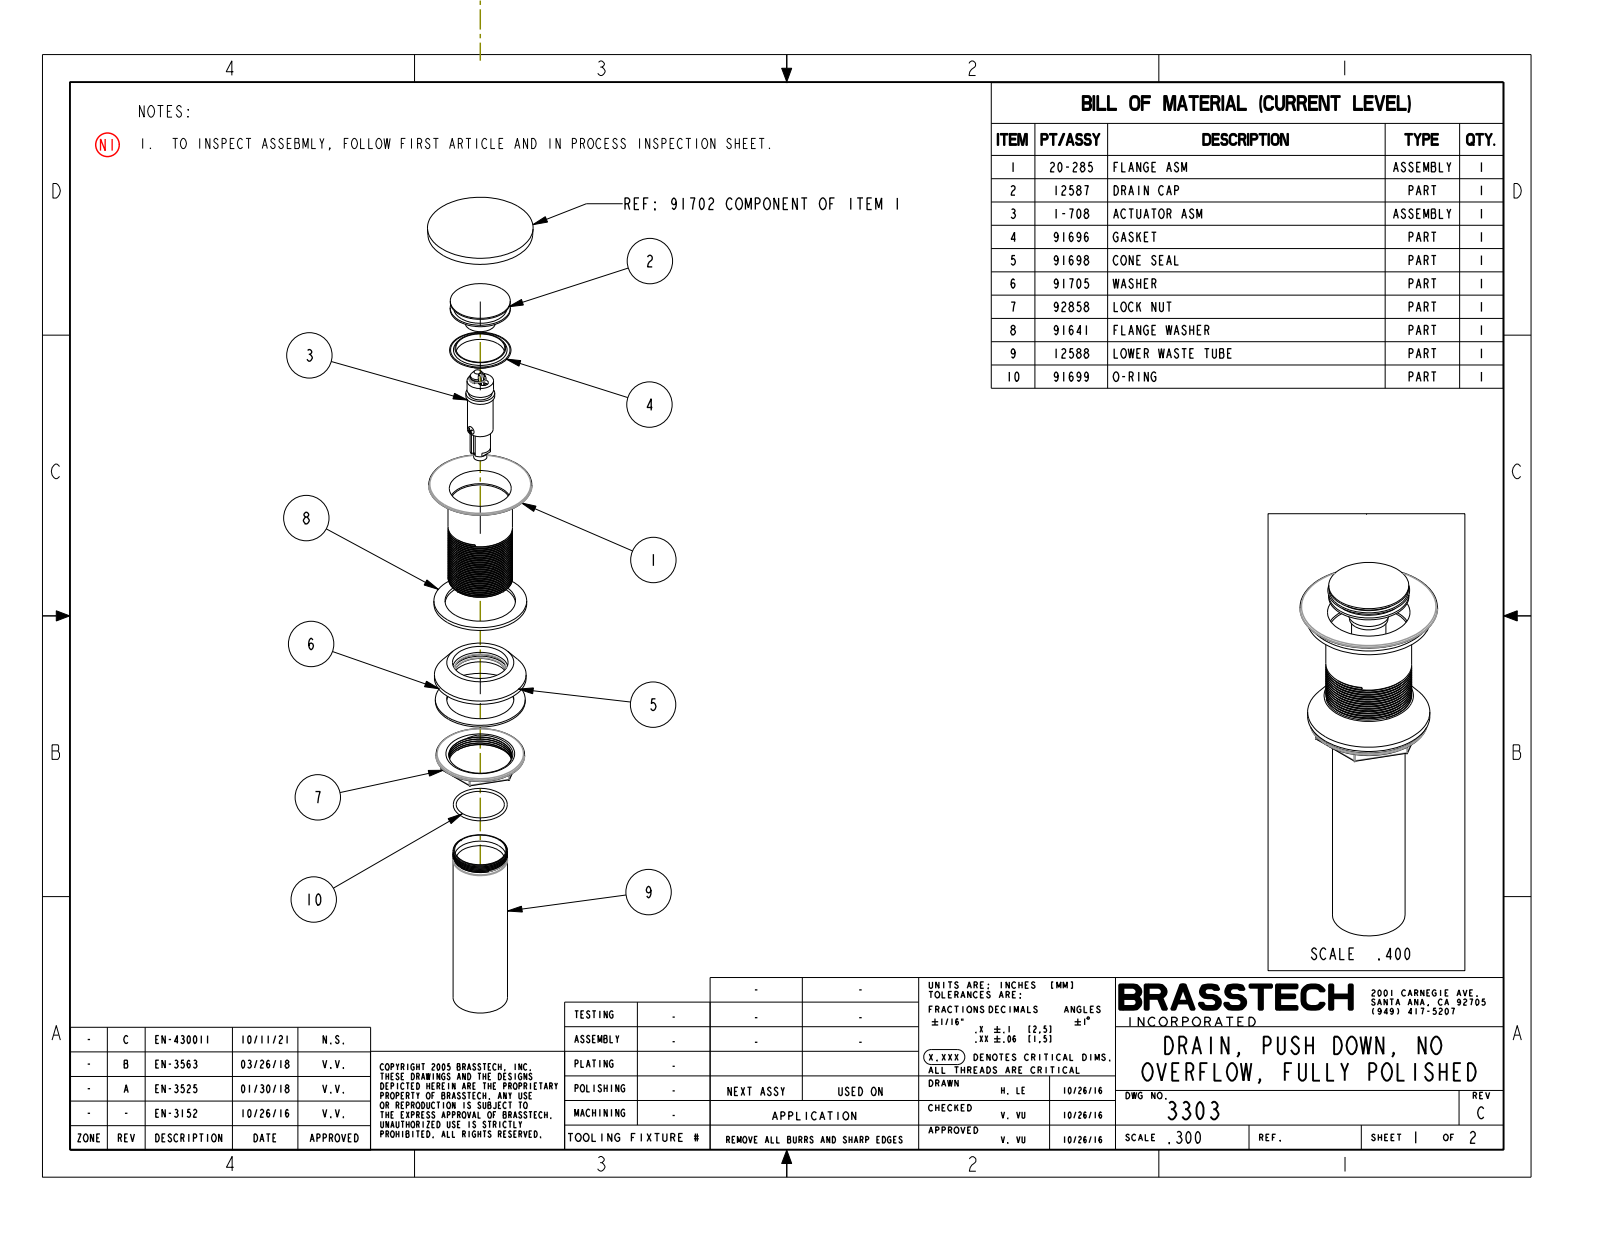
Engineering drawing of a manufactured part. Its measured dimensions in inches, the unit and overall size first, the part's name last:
Units: inches
Overall size (bounding box): 7.012 × 2.362 × 2.362
Round holes (diameter × count): ⌀1.176 ×1, ⌀1.181 ×1, ⌀1.228 ×1, ⌀1.28 ×1, ⌀1.339 ×1, ⌀1.378 ×1, ⌀1.417 ×1, ⌀1.44 ×1, ⌀1.535 ×1, ⌀1.614 ×1
Round bosses / shafts (diameter × count): ⌀0.05 ×3, ⌀2.362 ×1, ⌀2.126 ×1, ⌀2.1 ×1, ⌀2.059 ×1, ⌀2.028 ×1, ⌀1.476 ×1, ⌀1.376 ×1
Partial cylindrical surfaces — rounded edges, fillets, slot ends (radius × count): R0.02 ×18, R0.059 ×4
Main face-to-face distances: 0.079, 1.42, 1.341, 0.047, 0.205, 1.546, 1.625, 0.158, 1.499, 1.578
Volume: 7.638 in³ · Surface area: 104.3 in²
Bodies: 3 solids, 289 faces (46 planar, 134 cylindrical, 109 other)
Part name (STEP PRODUCT): 3303
STEP written by: CREO PARAMETRIC BY PTC INC, 2018500 (CONFIG_CONTROL_DESIGN)
